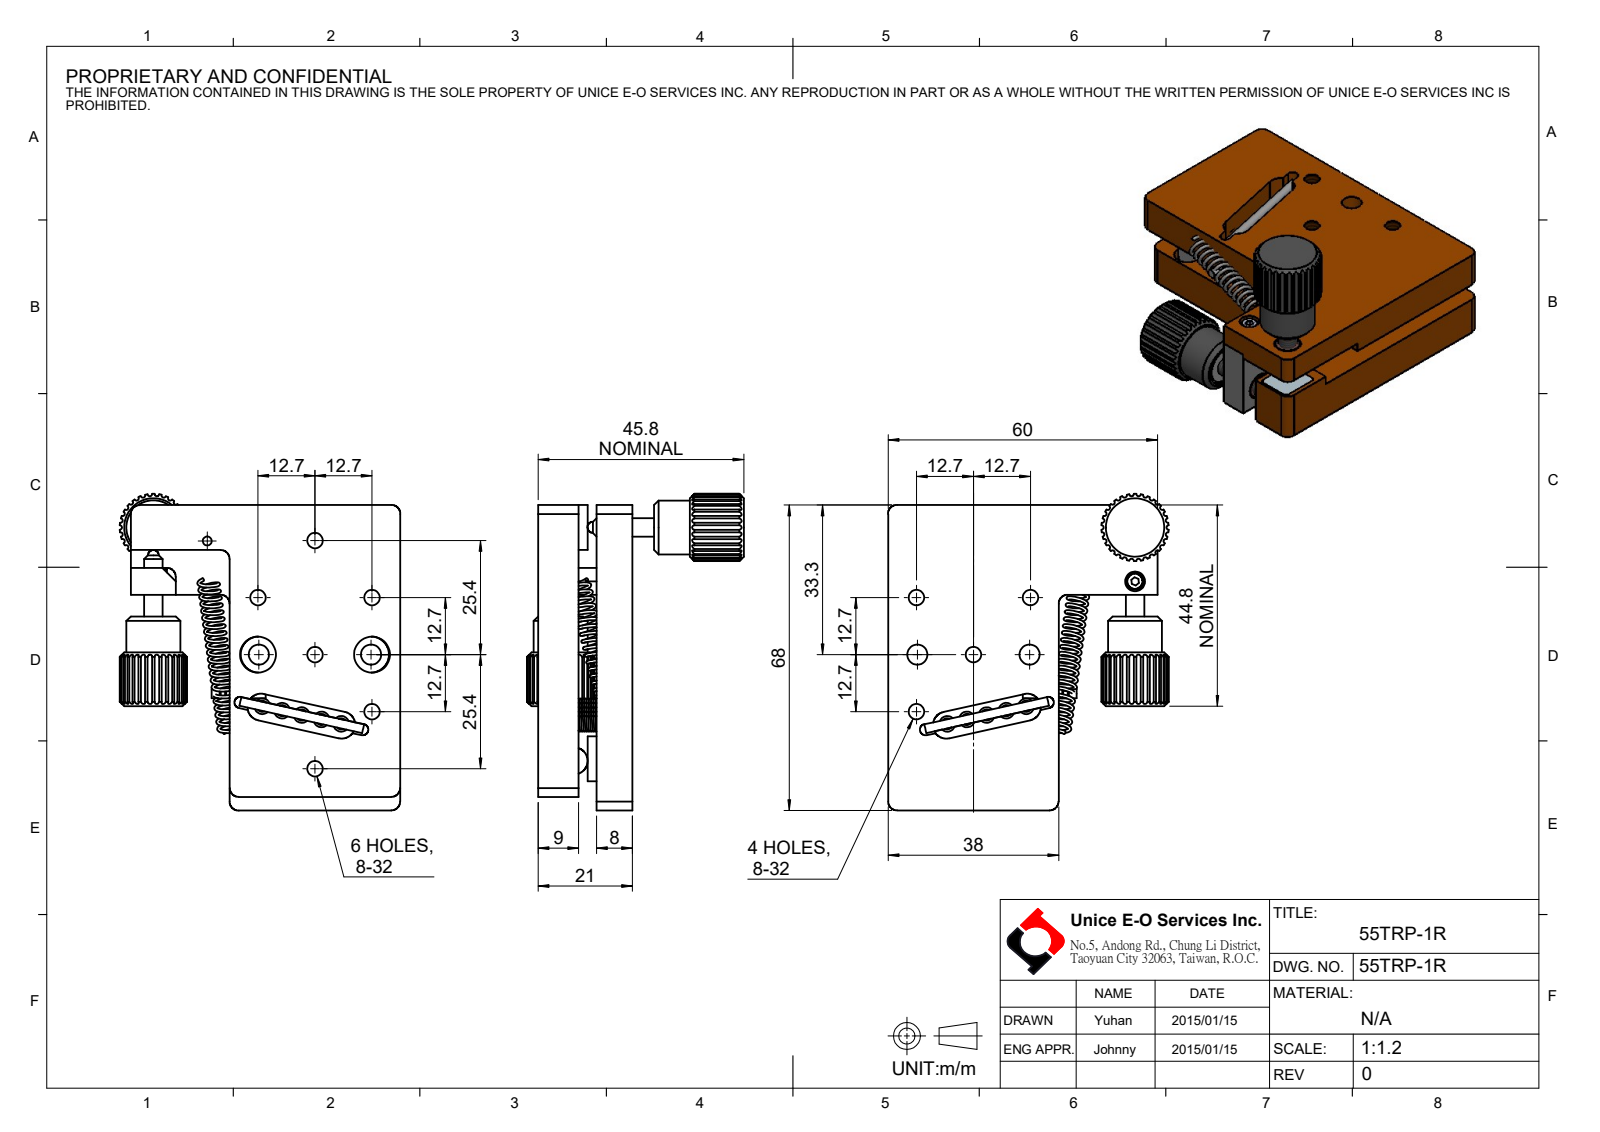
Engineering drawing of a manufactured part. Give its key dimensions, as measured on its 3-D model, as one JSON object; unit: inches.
{"part_name": "55TRP-1R", "step_written_by": "SolidWorks 2016 (CONFIG_CONTROL_DESIGN)", "units": "inches", "bodies": {"solids": 25, "faces": 519, "planar": 136, "cylindrical": 304, "other": 79}, "overall_size": [2.776, 2.46, 1.902], "volume_in3": 3.013, "surface_area_in2": 40.64, "round_holes": [[0.136, 8], [0.315, 4], [0.13, 3], [0.079, 2], [0.177, 2], [0.236, 2], [0.354, 2], [0.063, 1], [0.094, 1], [0.173, 1], [0.197, 1]], "round_bosses_or_shafts": [[0.079, 3], [0.472, 2], [0.236, 2], [0.161, 2], [0.15, 1], [0.098, 1], [0.047, 1]], "partial_cylinders_radius": [[0.02, 60], [0.079, 9], [0.03, 8], [0.039, 8], [0.118, 6], [0.049, 2], [0.295, 2]], "face_to_face_distances": [0.472, 0.315, 0.157, 0.827, 0.354, 0.512, 0.236, 0.079, 1.496, 0.394], "hole_center_spacings": [0.5, 1.118, 0.707, 1, 1.115, 1.111, 1.581, 0.487]}
